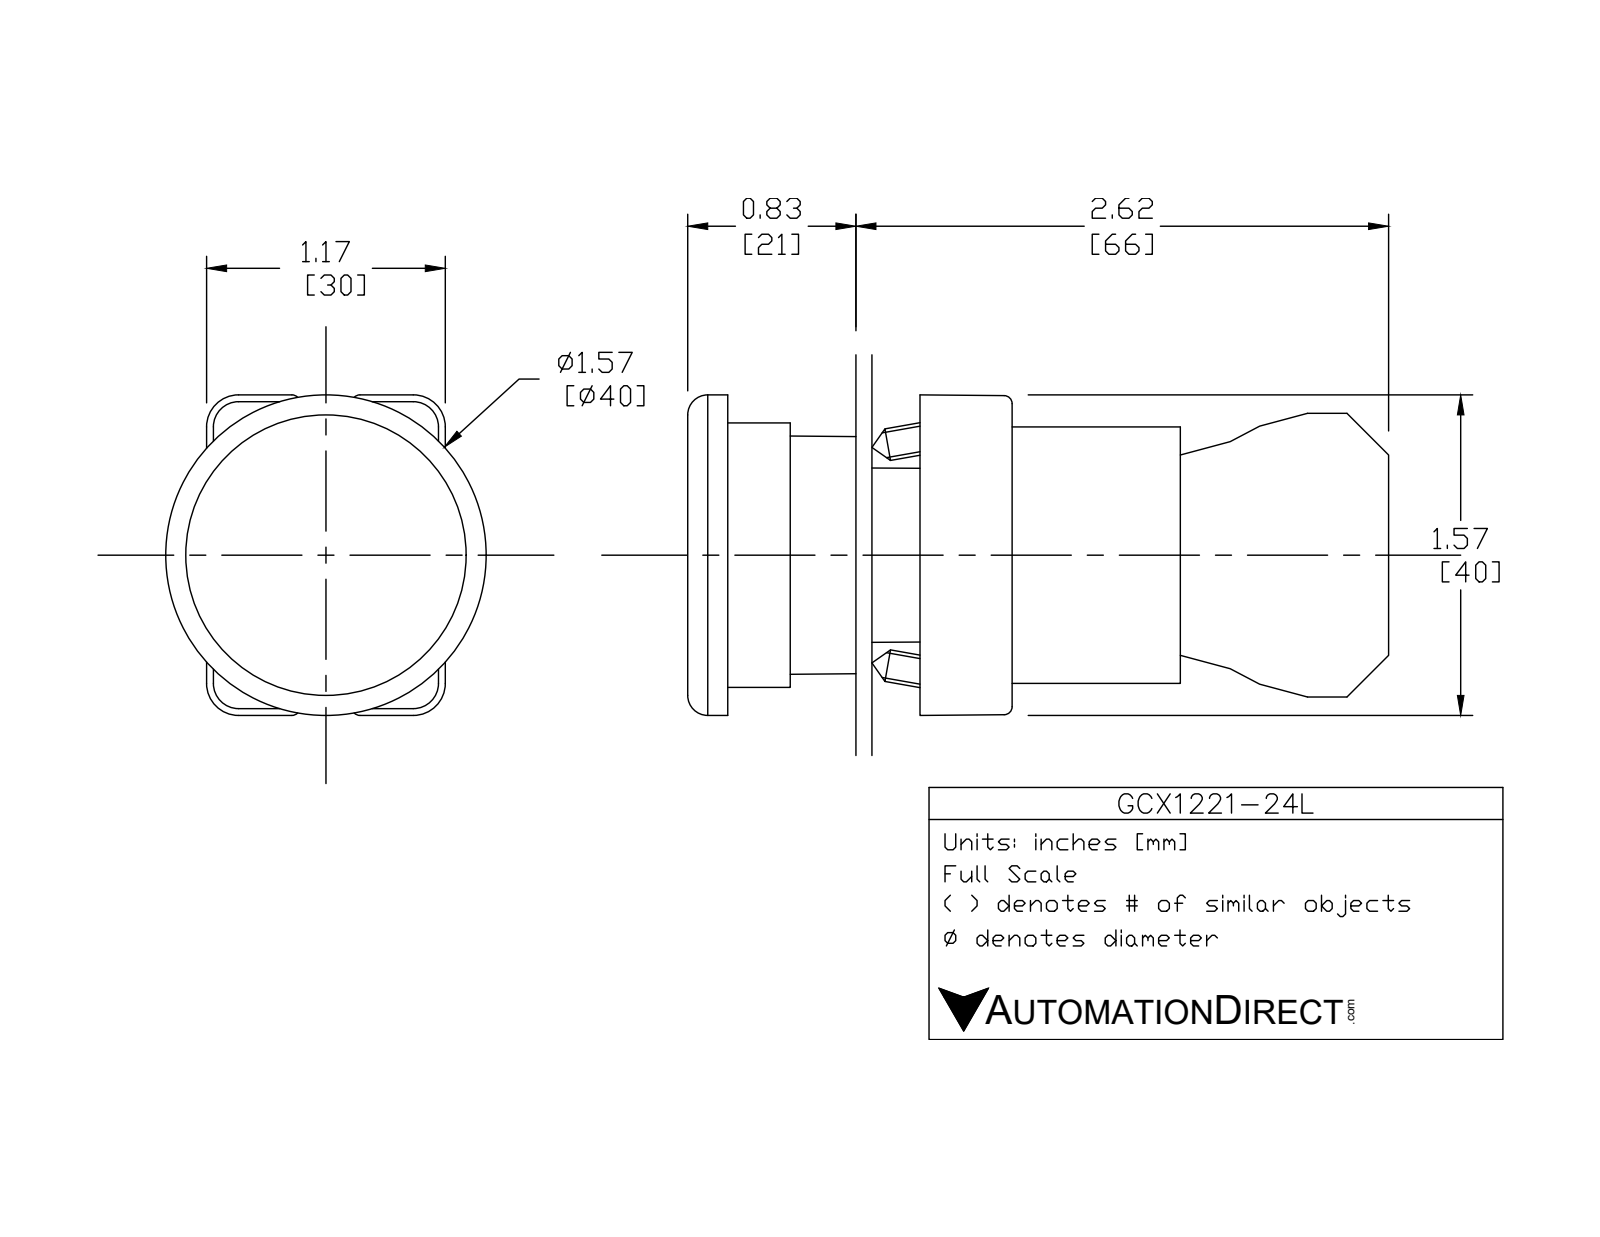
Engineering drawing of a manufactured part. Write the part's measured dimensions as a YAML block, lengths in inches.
part_name: "GCX122X OPERATOR; ecx1030; ECX1050; ECX1029-2 (+1 more)"
step_written_by: "SolidWorks 2016 (AUTOMOTIVE_DESIGN)"
units: inches
bodies: {solids: 7, faces: 431, planar: 252, cylindrical: 146, other: 33}
overall_size: [3.469, 1.581, 1.575]
volume: 2.895
surface_area: 40.89
round_holes:
  - {diameter: 0.079, count: 2}
  - {diameter: 0.124, count: 2}
  - {diameter: 0.13, count: 2}
  - {diameter: 0.087, count: 1}
  - {diameter: 0.197, count: 1}
  - {diameter: 0.469, count: 1}
  - {diameter: 0.878, count: 1}
  - {diameter: 0.888, count: 1}
  - {diameter: 1.024, count: 1}
  - {diameter: 1.181, count: 1}
round_bosses_or_shafts:
  - {diameter: 0.157, count: 4}
  - {diameter: 1.299, count: 1}
  - {diameter: 1.175, count: 1}
  - {diameter: 0.945, count: 1}
  - {diameter: 0.856, count: 1}
  - {diameter: 0.78, count: 1}
  - {diameter: 0.504, count: 1}
partial_cylinders:
  - {radius: 0.059, count: 24}
  - {radius: 0.041, count: 12}
  - {radius: 0.124, count: 12}
  - {radius: 0.157, count: 12}
  - {radius: 0.039, count: 8}
  - {radius: 0.128, count: 2}
  - {radius: 0.02, count: 1}
  - {radius: 0.063, count: 1}
face_to_face_distances: [0.827, 2.445, 1.618, 0.579, 2.287, 1.461, 0.157, 0.587, 0.031, 1.165]
hole_center_spacings: [0.236, 0.539, 0.472, 0.484]
